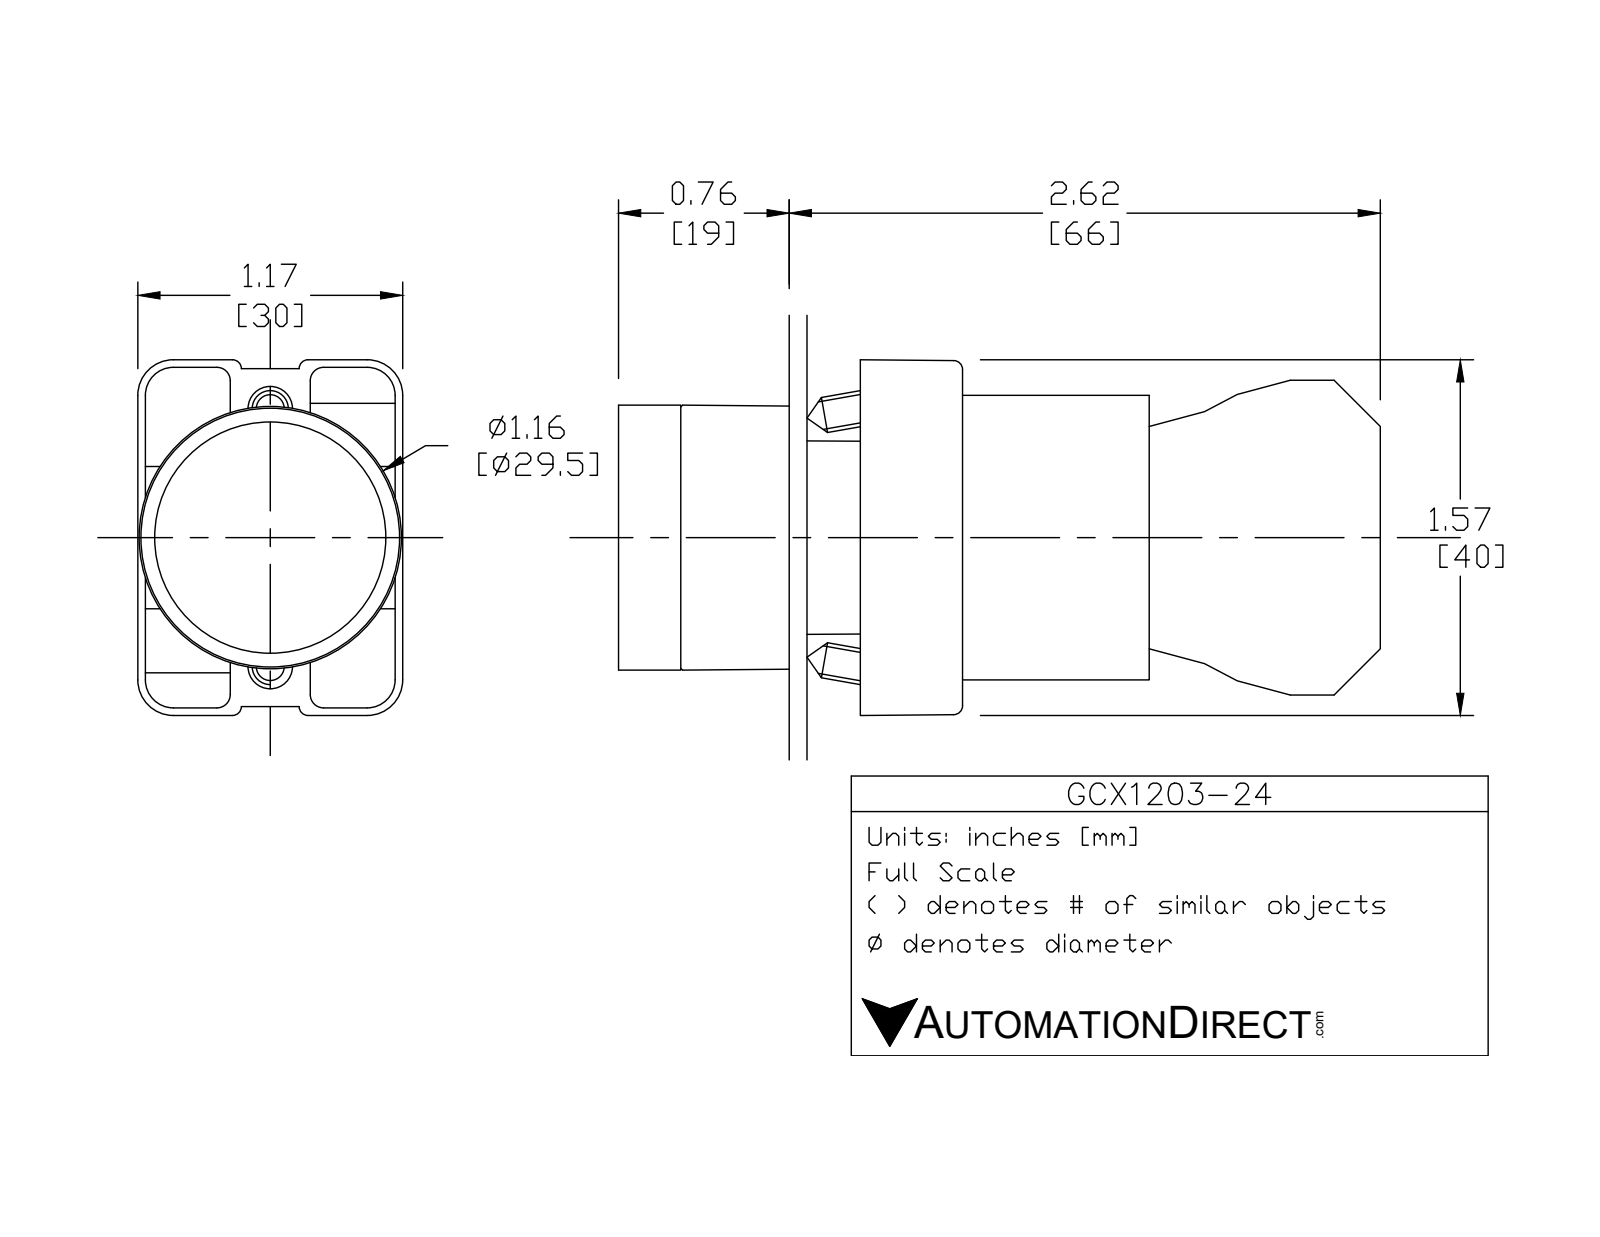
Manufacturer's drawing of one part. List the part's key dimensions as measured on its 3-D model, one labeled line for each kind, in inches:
Part name (STEP PRODUCT): ecx1040; ECX1050; ecx1029; GCX1203-24 (+1 more)
STEP written by: SolidWorks 2016 (AUTOMOTIVE_DESIGN)
Units: inches
Bodies: 8 solids, 431 faces (252 planar, 148 cylindrical, 31 other)
Overall size (bounding box): 3.319 × 1.581 × 1.177
Volume: 2.794 in³ · Surface area: 38.75 in²
Round holes (diameter × count): ⌀0.079 ×2, ⌀0.124 ×2, ⌀0.13 ×2, ⌀0.087 ×1, ⌀0.197 ×1, ⌀0.469 ×1, ⌀0.878 ×1, ⌀0.888 ×1, ⌀1.024 ×1
Round bosses / shafts (diameter × count): ⌀0.157 ×4, ⌀1.175 ×1, ⌀1.004 ×1, ⌀0.945 ×1, ⌀0.856 ×1, ⌀0.78 ×1, ⌀0.504 ×1
Partial cylindrical surfaces — rounded edges, fillets, slot ends (radius × count): R0.059 ×24, R0.041 ×12, R0.124 ×12, R0.157 ×12, R0.039 ×8, R0.128 ×2, R0.02 ×1, R0.063 ×1
Main face-to-face distances: 0.827, 2.02, 1.193, 0.579, 1.171, 0.031, 0.276, 0.033, 0.748, 0.573
Hole centre spacings: 0.236, 0.544, 0.472, 0.49
